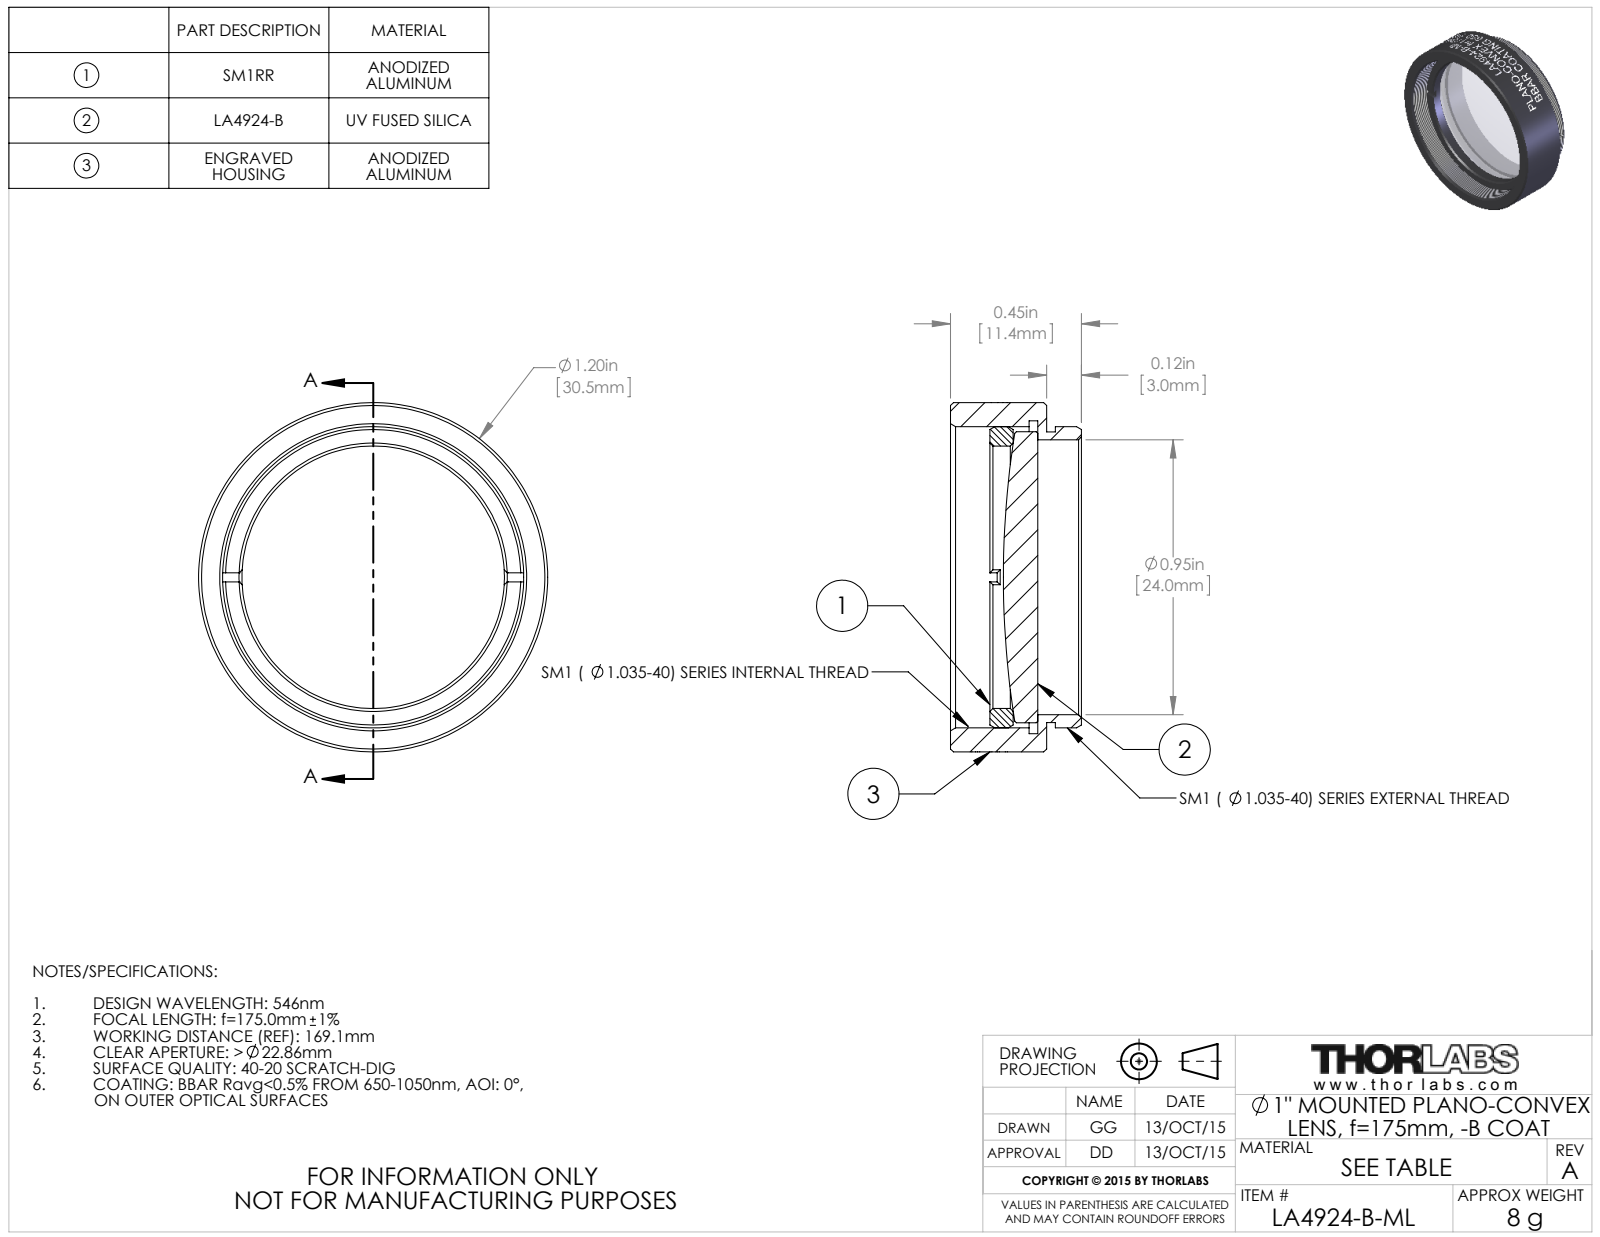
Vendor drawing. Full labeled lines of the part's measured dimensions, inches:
Part name (STEP PRODUCT): TTN039443-E0W
STEP written by: SolidWorks 2014 (CONFIG_CONTROL_DESIGN)
Units: inches
Bodies: 3 solids, 162 faces (20 planar, 114 cylindrical, 28 other)
Overall size (bounding box): 1.2 × 1.2 × 0.45
Volume: 0.204 in³ · Surface area: 6.671 in²
Round holes (diameter × count): ⌀0.902 ×1, ⌀0.945 ×1, ⌀1.075 ×1
Round bosses / shafts (diameter × count): ⌀1.2 ×1, ⌀1.035 ×1, ⌀1 ×1, ⌀0.999 ×1
Main face-to-face distances: 0.03, 0.33, 0.3, 0.115, 0.085, 0.215, 0.195, 0.165, 0.08, 0.135
